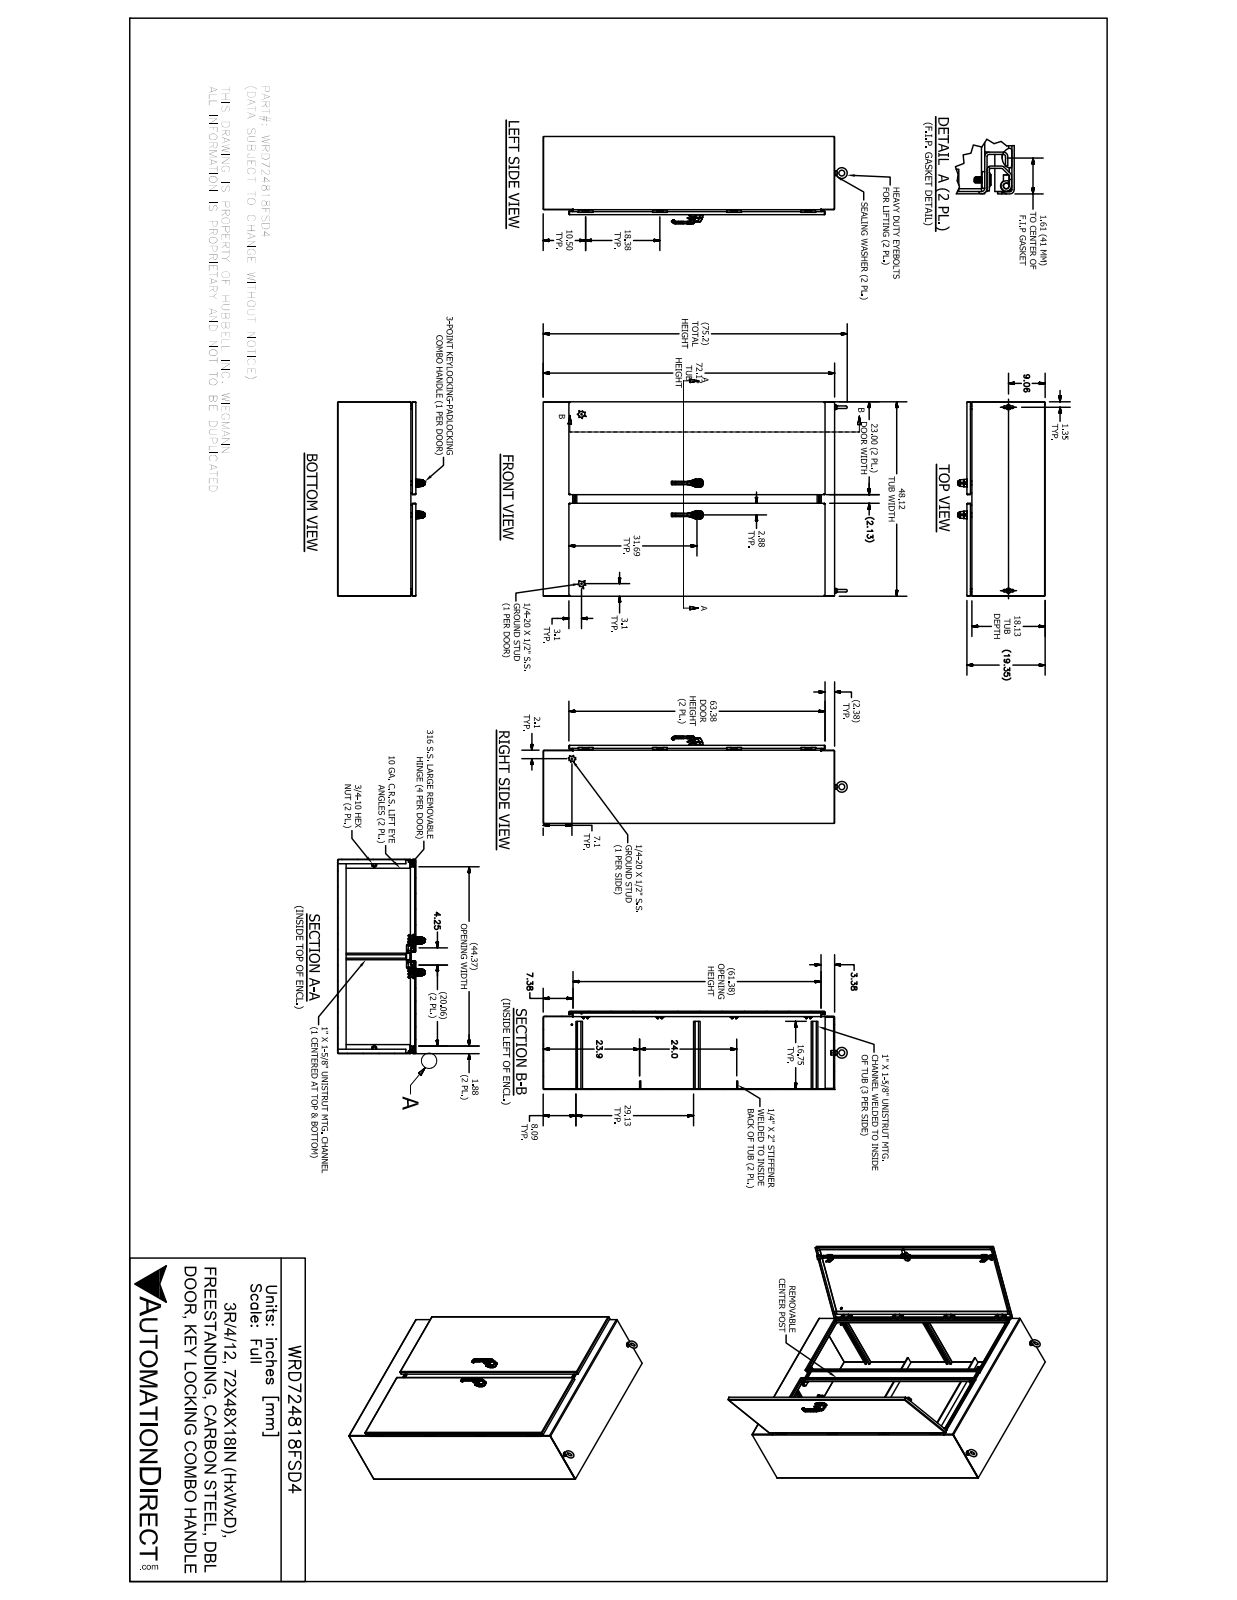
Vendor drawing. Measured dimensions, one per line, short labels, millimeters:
name: WRD724818FSD4_REPAIRED
written by: SolidWorks 2017 (AUTOMOTIVE_DESIGN)
unit: mm
bodies: 155 solids, 3246 faces (1520 planar, 1090 cylindrical, 636 other)
size: 1911.3 × 1222.6 × 546.8
volume: 26 140 000 mm³; area: 18 590 000 mm²
holes: 20× ⌀6.8, 16× ⌀5.8, 16× ⌀7.1, 16× ⌀16.5, 8× ⌀5.1, 8× ⌀7, 6× ⌀7.1, 4× ⌀4, 4× ⌀6.4, 4× ⌀10.2, 4× ⌀11.4, 3× ⌀6.1
bosses: 15× ⌀15.9, 13× ⌀6.4, 4× ⌀13.5, 4× ⌀11.1, 4× ⌀9.5, 4× ⌀8, 4× ⌀5.4, 3× ⌀25.4
rounds: 43× R1.6, 32× R1.3, 32× R3.2, 17× R1.6, 16× R0.3, 16× R0.5, 16× R0.6, 16× R1.3
face distances: 2.6, 488.8, 486.2, 491.5, 1219.7, 1829.3, 1217.1, 457.7, 31.1, 1222.4
hole spacings: 25.4, 466.7, 933.5, 1278.8, 466.7, 1190.6, 1190.9, 1278.8
